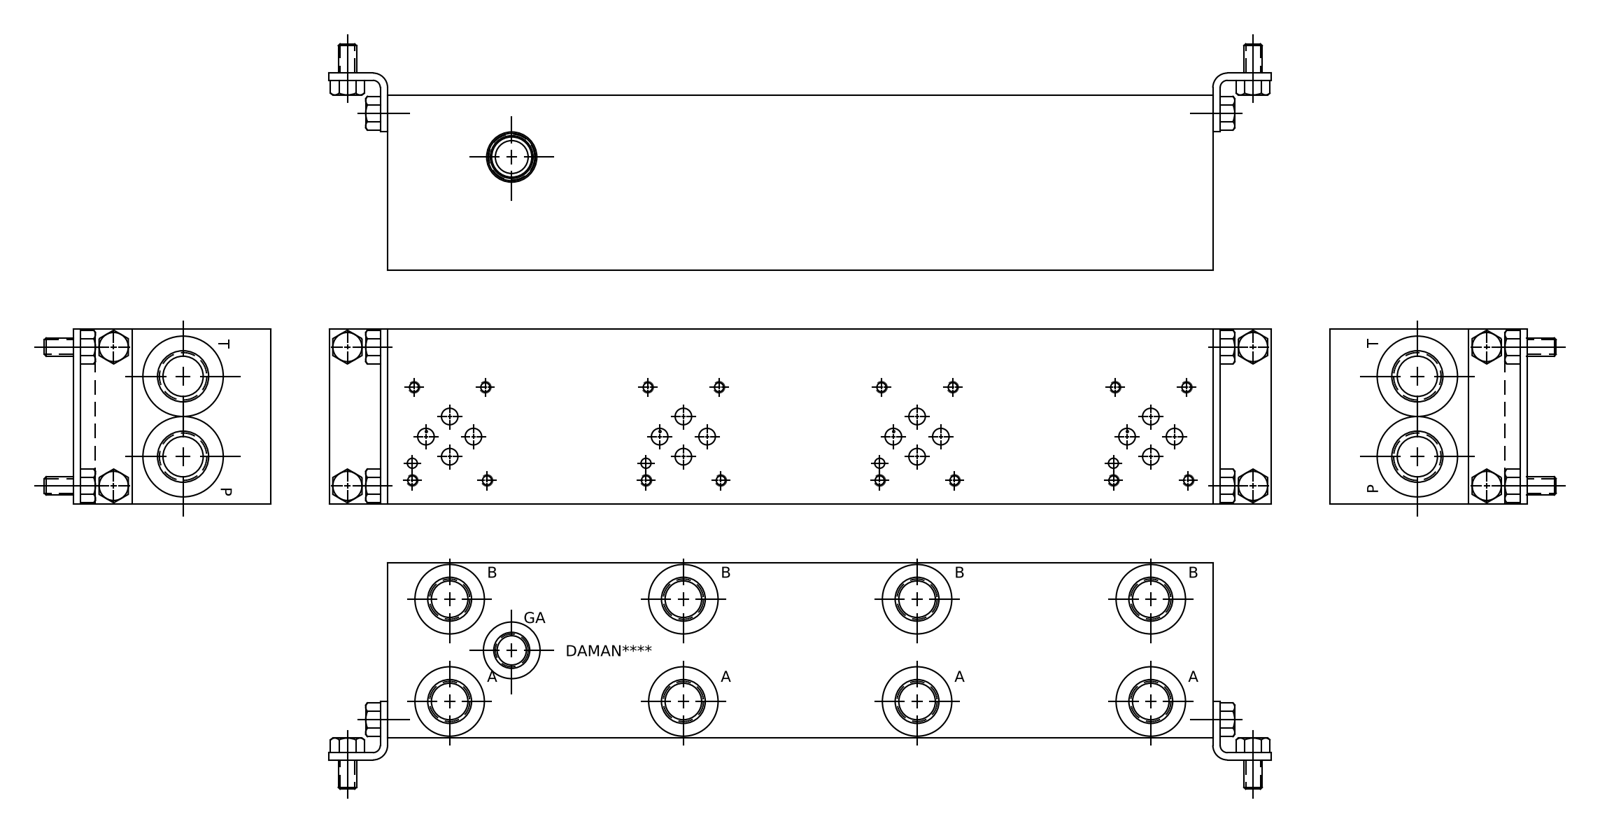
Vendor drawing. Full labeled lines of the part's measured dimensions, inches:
Part name (STEP PRODUCT): Part_AD03P044S~S_3D
STEP written by: Autodesk Inventor 2021 (AUTOMOTIVE_DESIGN)
Units: inches
Bodies: 1 solid, 867 faces (450 planar, 134 cylindrical, 283 other)
Overall size (bounding box): 14.125 × 3 × 3
Volume: 119.9 in³ · Surface area: 231.7 in²
Round holes (diameter × count): ⌀0.149 ×16, ⌀0.19 ×16, ⌀0.281 ×12, ⌀0.563 ×8, ⌀0.689 ×8, ⌀0.75 ×8, ⌀0.758 ×8, ⌀1.206 ×8, ⌀0.156 ×4, ⌀0.25 ×4, ⌀0.257 ×2, ⌀0.312 ×2
Main face-to-face distances: 3, 0.031, 14.125, 2.969, 0.031, 14.094, 14.094, 14.063, 0.562, 2.407
Hole centre spacings: 4, 8, 12, 3.609, 3.611, 4.059, 4.366, 4.419
